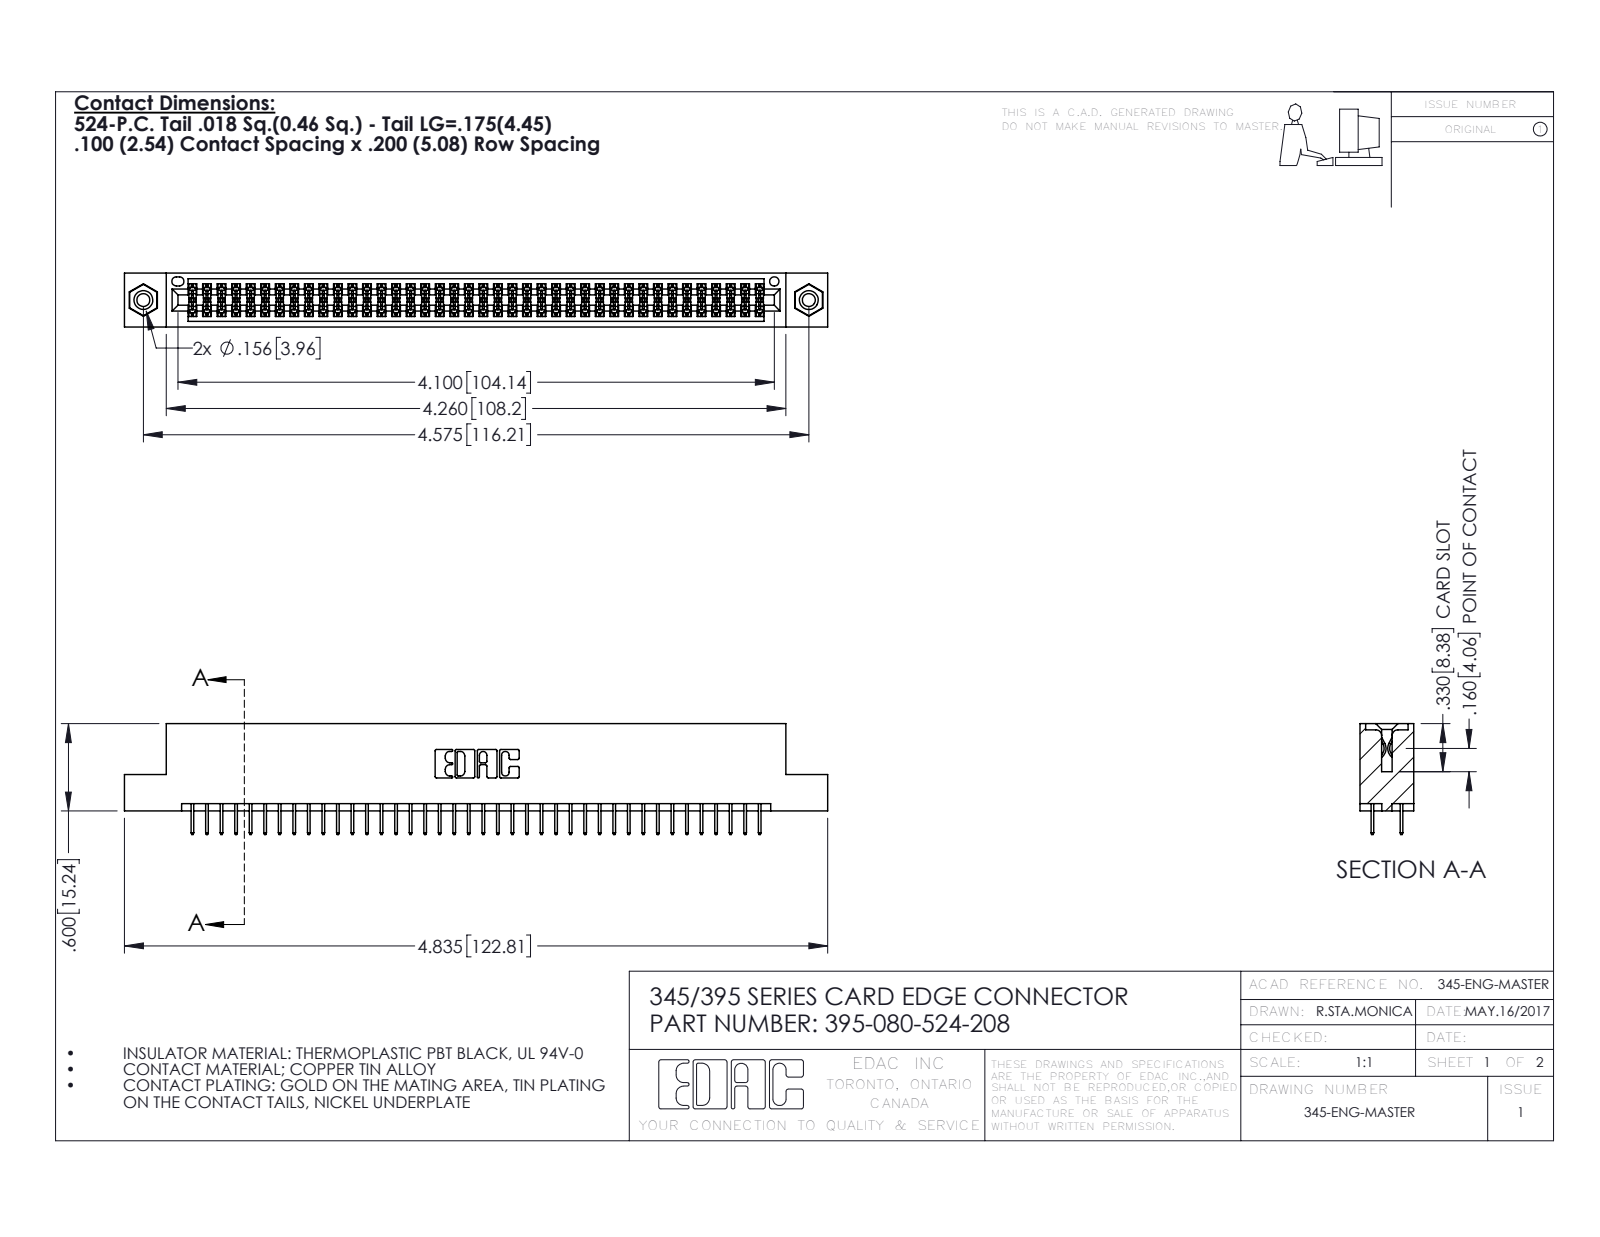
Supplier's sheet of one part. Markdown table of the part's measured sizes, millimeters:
| quantity | value |
| --- | --- |
| part name | 345 Part_Flush Mounting Lugs - 0.156 Dia-TI; 395-080-524-208; 345-250-001_345-250-003-102; 345-292-001_345-293-124 |
| STEP written by | SolidWorks 2016 (CONFIG_CONTROL_DESIGN) |
| units | millimeters |
| bodies | 83 solids, 4506 faces (3232 planar, 1258 cylindrical, 16 other) |
| overall size | 122.8 × 19.4 × 9.4 |
| volume | 11 800 mm³ |
| surface area | 17 070 mm² |
| round holes (diameter × count) | 2.3 × 2, 3.2 × 2, 4 × 2, 1.6 × 1 |
| round bosses / shafts (diameter × count) | 3.9 × 2 |
| partial cylindrical surfaces (radius × count) | 0.2 × 120, 0.3 × 22, 0.2 × 6, 0.8 × 6, 0.7 × 3, 0.4 × 2, 0.5 × 2, 0.6 × 2 |
| main face-to-face distances | 1.8, 7.6, 5.1, 9.4, 2.5, 6.9, 0.6, 5.7, 1.8, 4.4 |
| hole center spacings | 6.9, 110.2, 116.2 |
